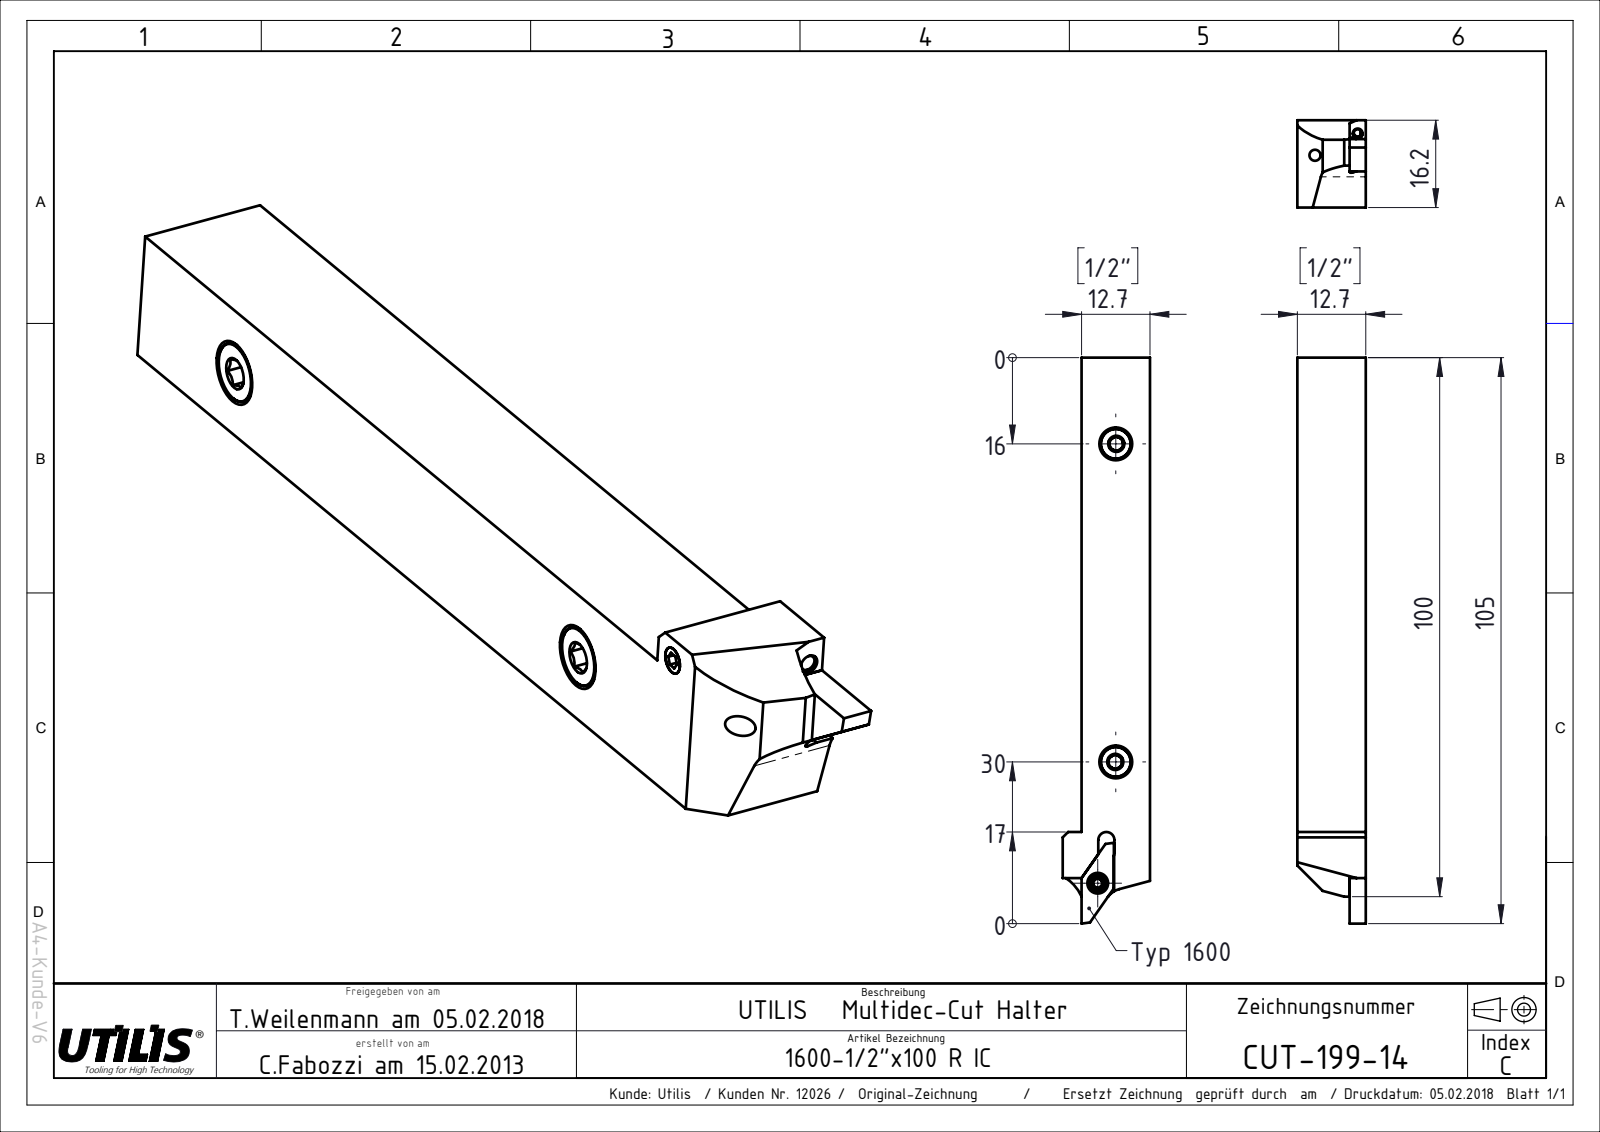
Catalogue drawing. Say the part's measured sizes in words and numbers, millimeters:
The part is named "CUT-199-14". Its 3-D file was written by "SolidWorks 2015 (AUTOMOTIVE_DESIGN)". It is 1 solid with 55 faces: 46 planar, 6 cylindrical and 3 other. Overall it measures 105 by 16.2 by 12.7 millimeters. Its volume is 16 111 cubic millimeters and its surface area 5 515 square millimeters. Partial cylindrical surfaces (rounded edges, fillets, slot ends): 2 of radius 1.5, 1 of radius 0.25, 1 of radius 4. The main face-to-face distances are 12.7, 16.2, 3.5, 3, 88, 6, 9.7, 6.7, 9.5, 6.6.
